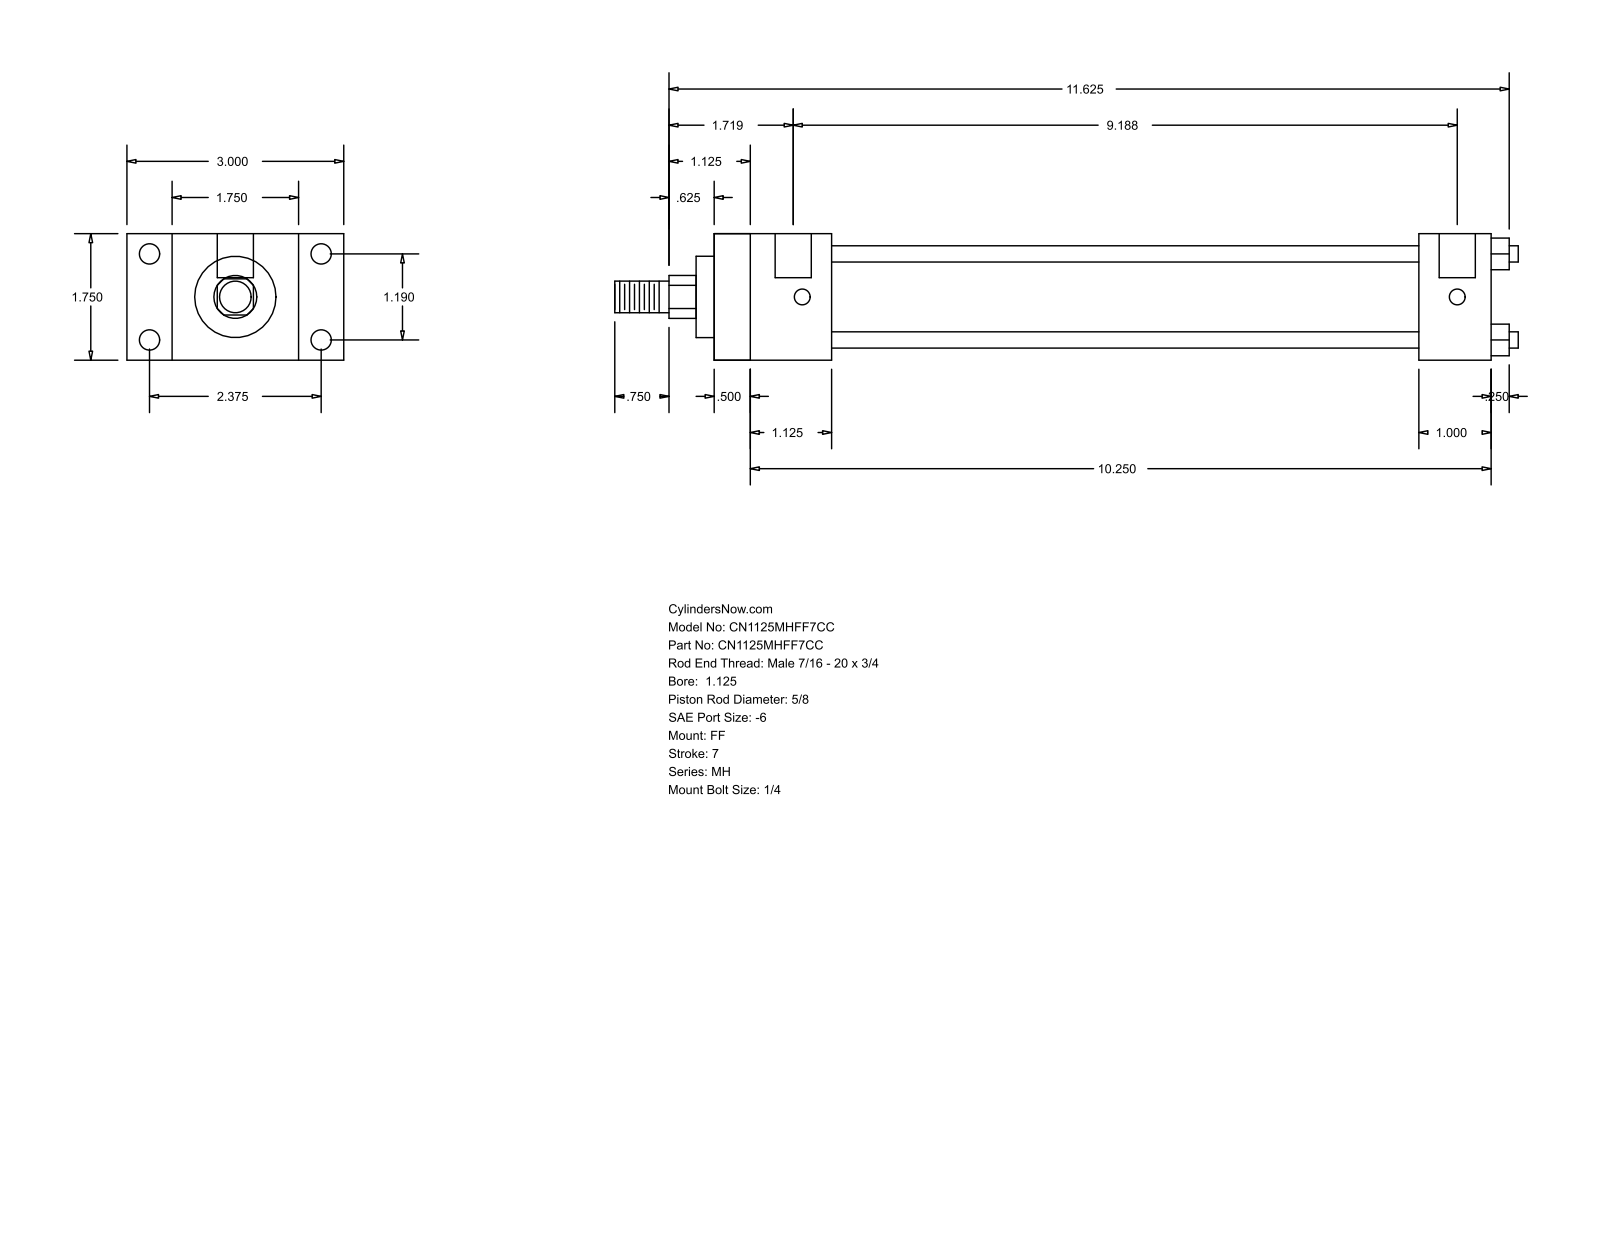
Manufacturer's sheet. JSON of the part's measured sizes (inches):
{"part_name": "MH_FF__0112_0.625", "step_written_by": "GSSL Pune (CONFIG_CONTROL_DESIGN)", "units": "inches", "bodies": {"solids": 0, "faces": 92, "planar": 64, "cylindrical": 28, "other": 0}, "overall_size": [12.5, 3, 1.75], "round_holes": [[0.219, 4], [0.281, 4], [0.5, 2]], "round_bosses_or_shafts": [[0.225, 4], [1.375, 1], [1.125, 1], [0.625, 1], [0.437, 1]], "partial_cylinders_radius": [[0.297, 1]], "face_to_face_distances": [1.75, 10.75, 0.5, 10.25, 0.625, 1.125, 2.375, 1.625, 9.75, 9.25], "hole_center_spacings": [1.19, 2.375, 2.656, 9.063, 0.125, 9.187]}
